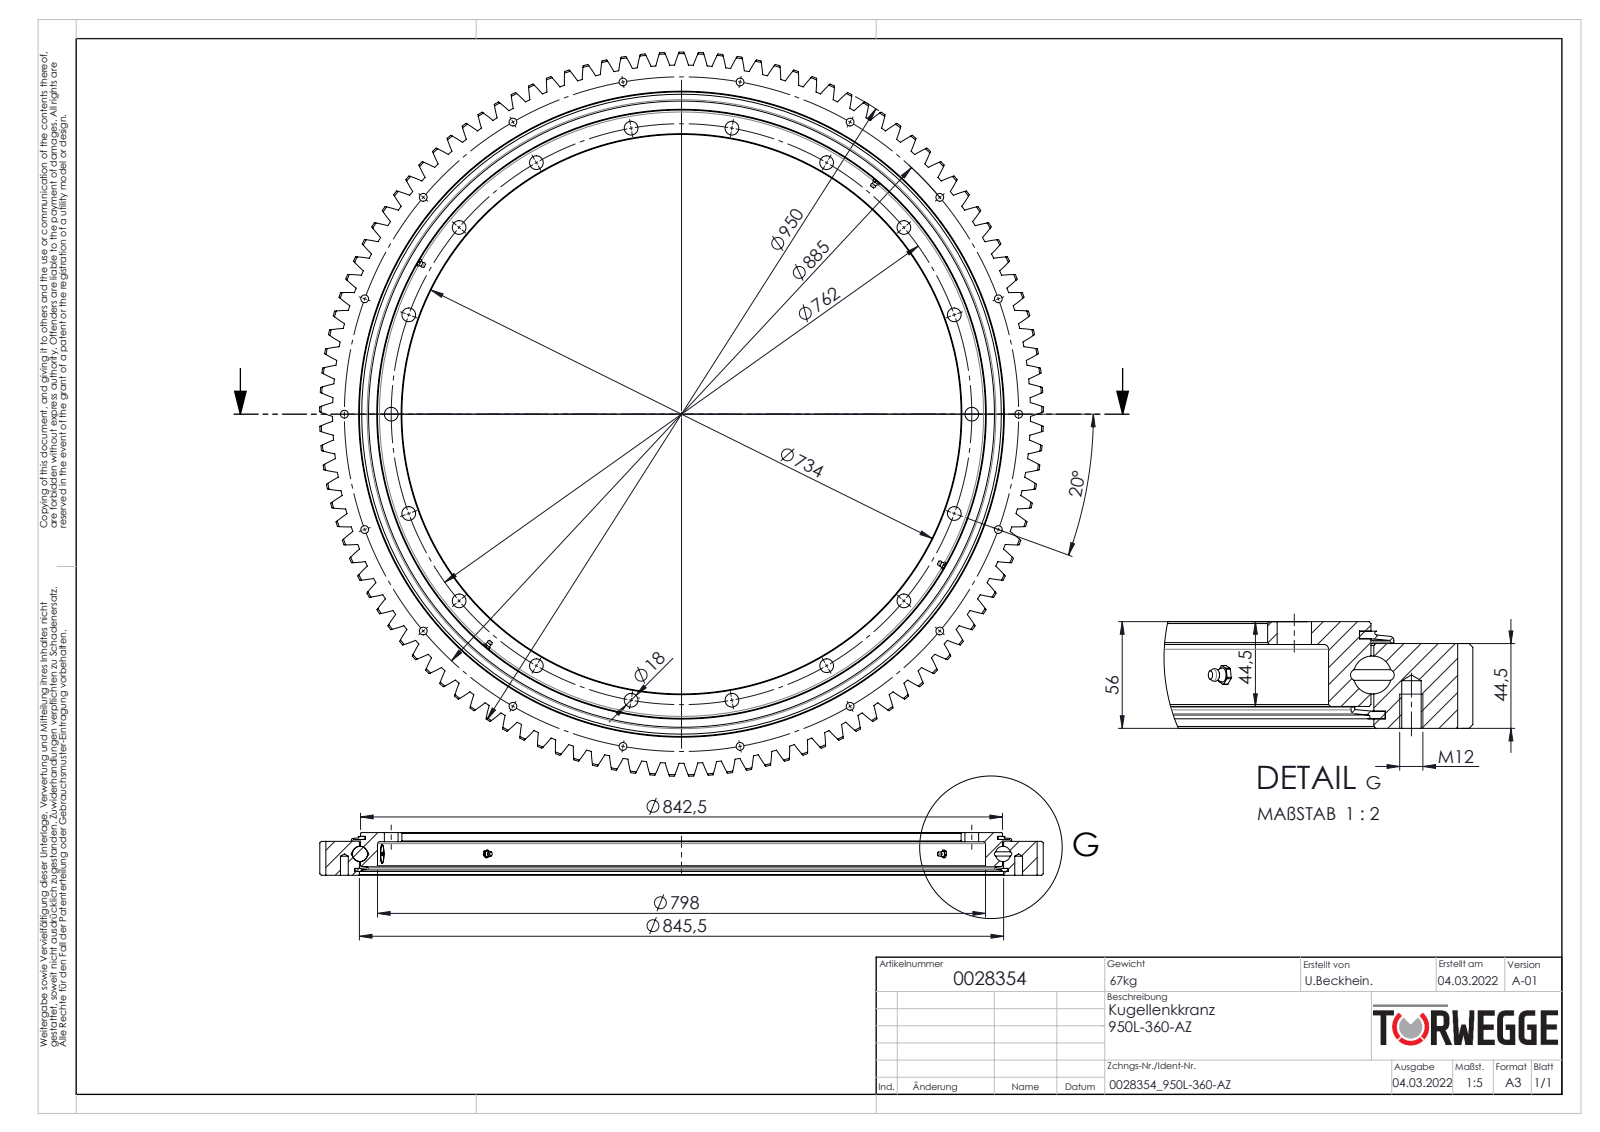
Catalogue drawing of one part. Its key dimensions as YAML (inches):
part_name: "0028354"
step_written_by: "SolidWorks 2020 (AUTOMOTIVE_DESIGN)"
units: inches
bodies: {solids: 6, faces: 1071, planar: 57, cylindrical: 625, other: 389}
overall_size: [37.401, 37.398, 2.205]
volume: 501.4
surface_area: 2322
round_holes:
  - {diameter: 0.402, count: 18}
  - {diameter: 0.709, count: 18}
  - {diameter: 0.268, count: 4}
  - {diameter: 0.157, count: 1}
  - {diameter: 0.197, count: 1}
  - {diameter: 0.984, count: 1}
  - {diameter: 28.898, count: 1}
  - {diameter: 31.417, count: 1}
  - {diameter: 32.343, count: 1}
  - {diameter: 32.698, count: 1}
  - {diameter: 33.287, count: 1}
  - {diameter: 33.76, count: 1}
round_bosses_or_shafts:
  - {diameter: 0.268, count: 4}
  - {diameter: 34.114, count: 1}
  - {diameter: 33.759, count: 1}
  - {diameter: 33.169, count: 1}
  - {diameter: 32.697, count: 1}
  - {diameter: 32.5, count: 1}
  - {diameter: 0.984, count: 1}
partial_cylinders:
  - {radius: 7.37, count: 234}
  - {radius: 0.197, count: 4}
  - {radius: 18.031, count: 1}
  - {radius: 18.701, count: 1}
face_to_face_distances: [0.453, 1.752, 2.205, 1.654, 1.732, 0.02, 0.472, 0.157, 1.28, 1.299]
hole_center_spacings: [17.421, 11.32, 16.346, 30.477, 15, 6.05, 20.922, 11.917]
